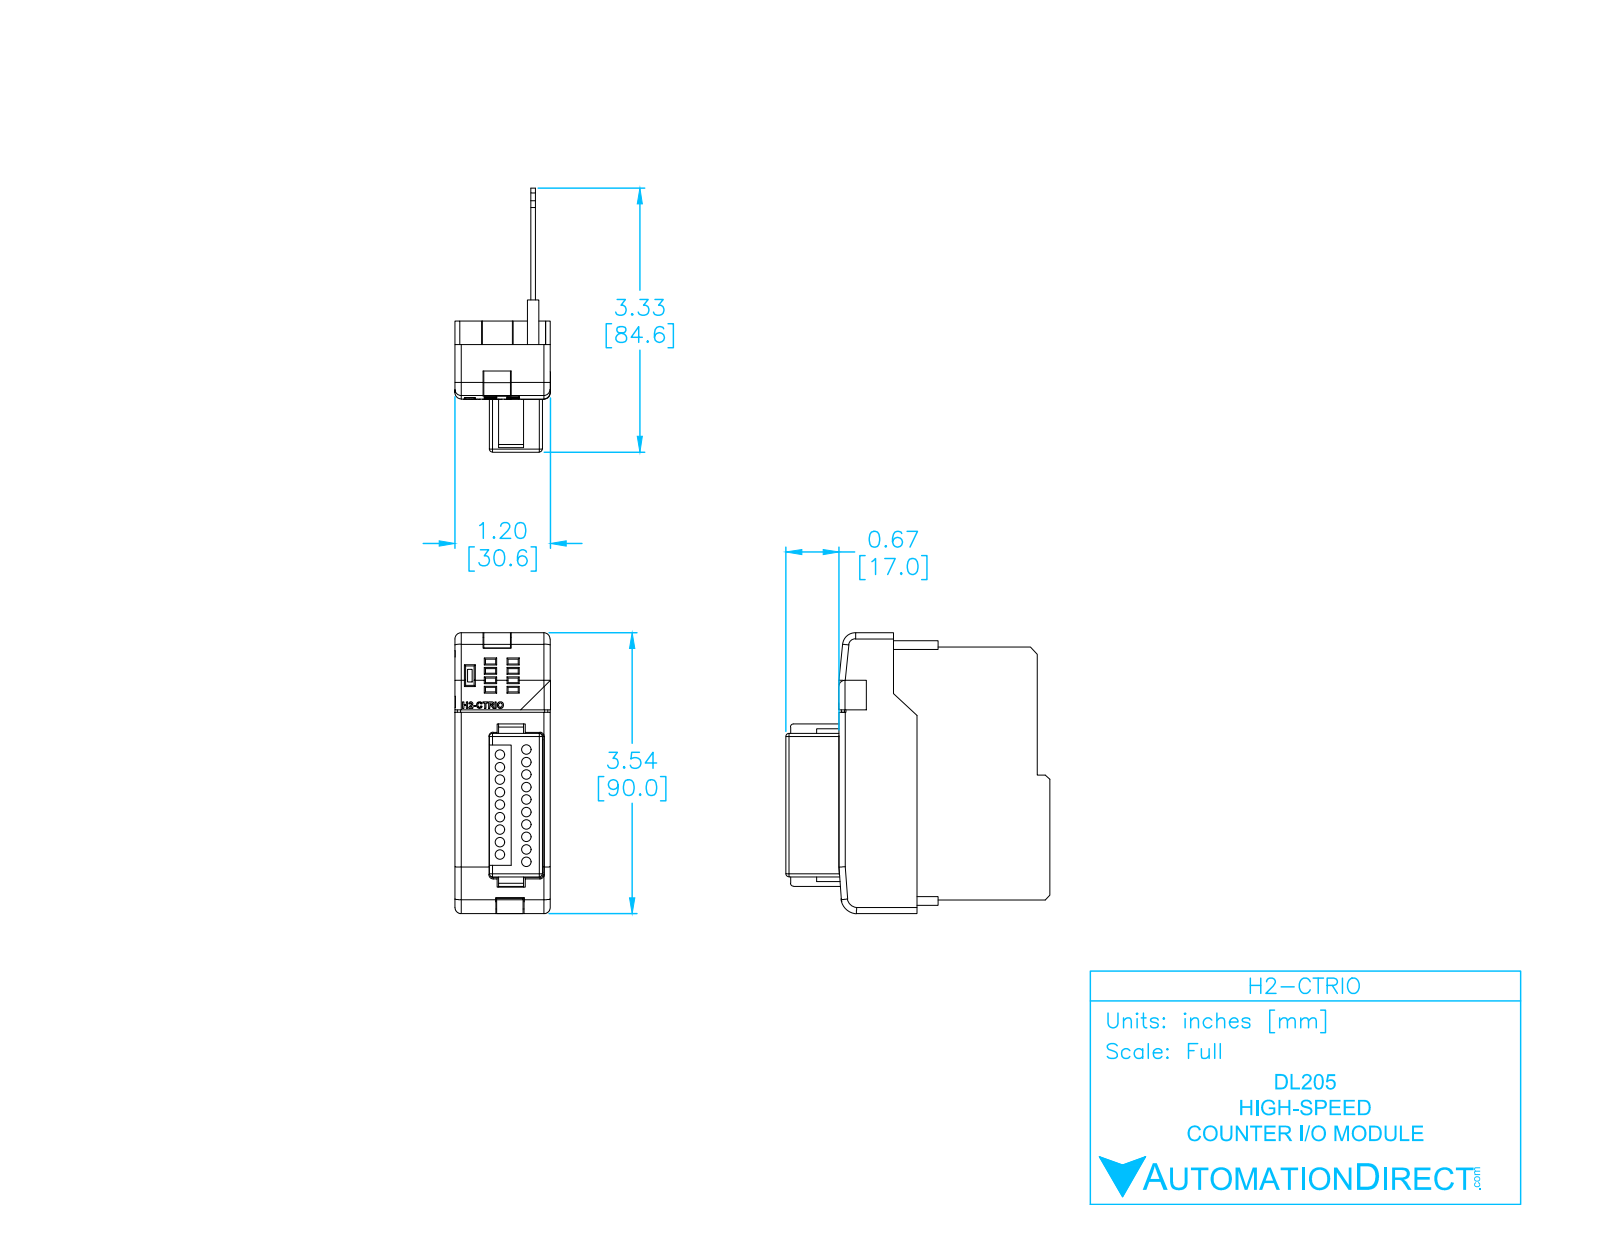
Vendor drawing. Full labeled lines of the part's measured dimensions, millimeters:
Part name (STEP PRODUCT): H2-CTRIO_ModuleCase_New
STEP written by: SolidWorks 2009 (AUTOMOTIVE_DESIGN)
Units: millimetres
Bodies: 2 solids, 617 faces (405 planar, 158 cylindrical, 54 other)
Overall size (bounding box): 90 × 84.85 × 30.55
Volume: 30 589 mm³ · Surface area: 32 688 mm²
Round holes (diameter × count): ⌀3 ×19
Partial cylindrical surfaces — rounded edges, fillets, slot ends (radius × count): R0.35 ×28, R1 ×18, R0.5 ×12, R2 ×11, R0.25 ×6, R2.62 ×1, R3.79 ×1, R4.12 ×1
Main face-to-face distances: 1.5, 4.72, 3.22, 0.5, 6.22, 1, 24.28, 29, 18, 11
Hole centre spacings: 4, 8, 12, 16, 8.61, 8.77, 20, 10.16
